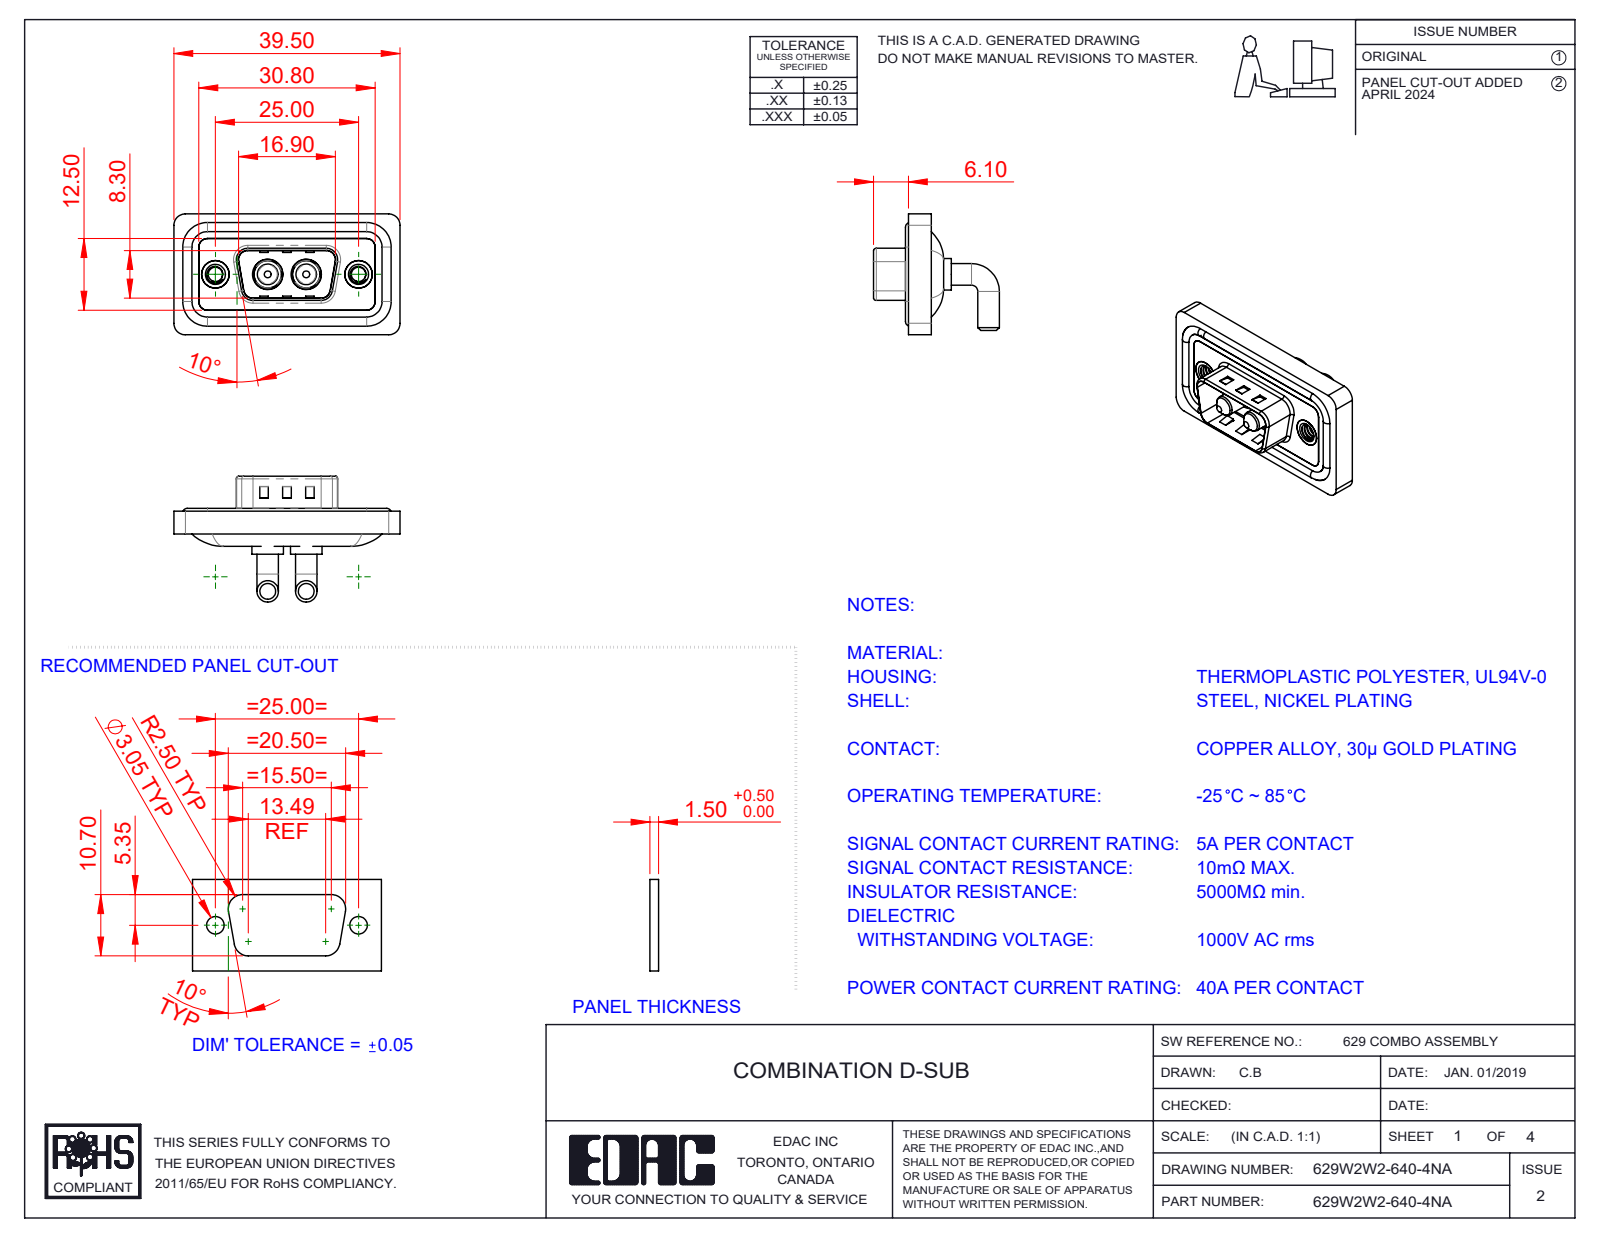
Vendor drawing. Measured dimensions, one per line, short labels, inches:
name: Power Pin_40A RA; 629Combo Threaded Rivet_A; 629Combo Waterproof Housing_09 Contacts; 629Combo Housing_2W2 (+3 more)
written by: SolidWorks 2023 (CONFIG_CONTROL_DESIGN)
unit: in
bodies: 11 solids, 491 faces (165 planar, 220 cylindrical, 106 other)
size: 1.555 × 0.865 × 0.831
volume: 0.289 in³; area: 11.25 in²
holes: 2× ⌀0.098, 2× ⌀0.157, 2× ⌀0.189, 2× ⌀0.191, 2× ⌀0.197, 2× ⌀0.209
bosses: 4× ⌀0.148, 4× ⌀0.063, 2× ⌀0.217, 2× ⌀0.205, 2× ⌀0.193, 2× ⌀0.187, 2× ⌀0.142
rounds: 18× R0.059, 18× R0.079, 8× R0.02, 8× R0.063, 4× R0.01, 4× R0.024, 4× R0.026, 4× R0.035
face distances: 0.016, 0.114, 0.043, 0.031, 0.083, 0.098, 0.122, 0.063, 0.177, 0.059
hole spacings: 0.36, 0.624, 0.265, 0.984
